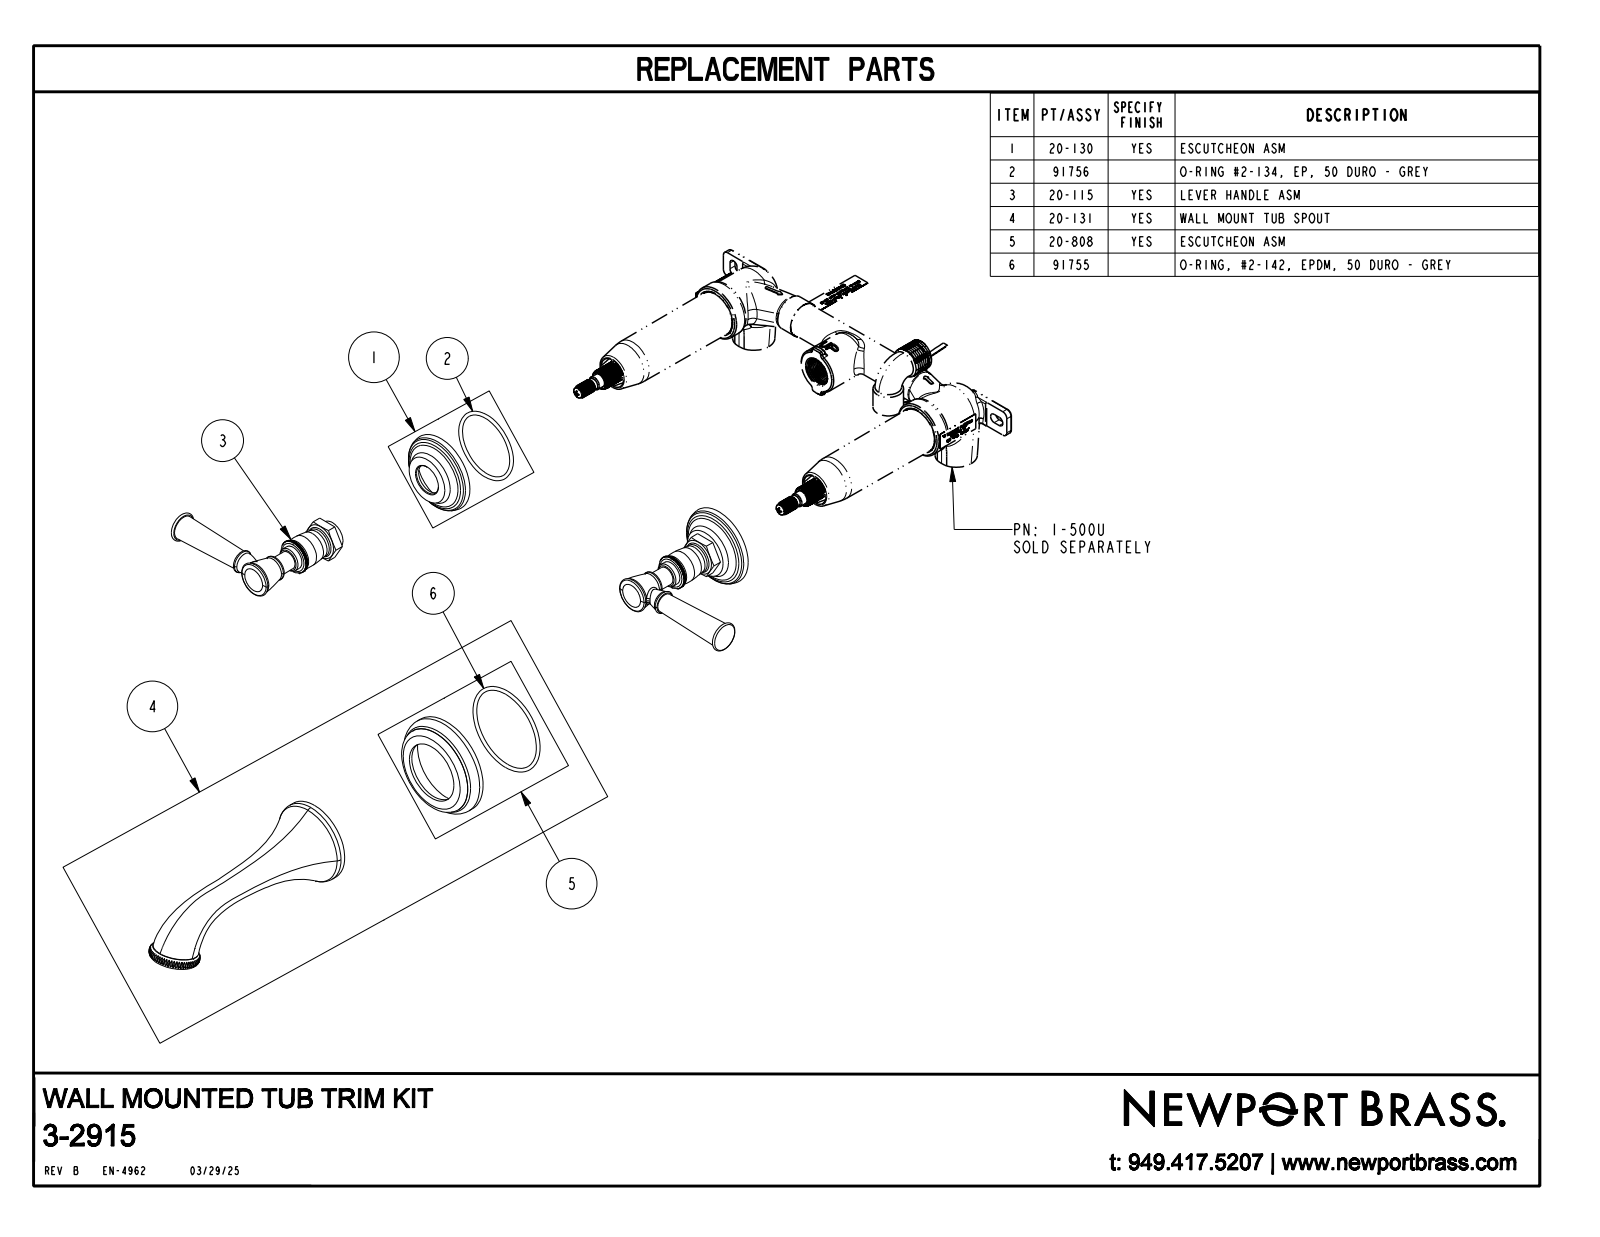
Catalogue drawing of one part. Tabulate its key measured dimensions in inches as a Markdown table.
| quantity | value |
| --- | --- |
| part name | 3-2915_SW0001 |
| STEP written by | CREO PARAMETRIC BY PTC INC, 2018400 (AUTOMOTIVE_DESIGN) |
| units | inches |
| bodies | 3 solids, 862 faces (520 planar, 18 cylindrical, 324 other) |
| overall size | 14.387 × 8.764 × 6.711 |
| volume | 18.56 in³ |
| surface area | 86.98 in² |
| round bosses / shafts (diameter × count) | 0.686 × 2, 0.53 × 2, 2.85 × 1, 2.506 × 1, 2.345 × 1, 1.198 × 1, 1.102 × 1 |
| main face-to-face distances | 0.534, 1.025, 6.82, 0.575, 0.041, 1.864, 1.33, 1.289, 0.509, 0.515 |
